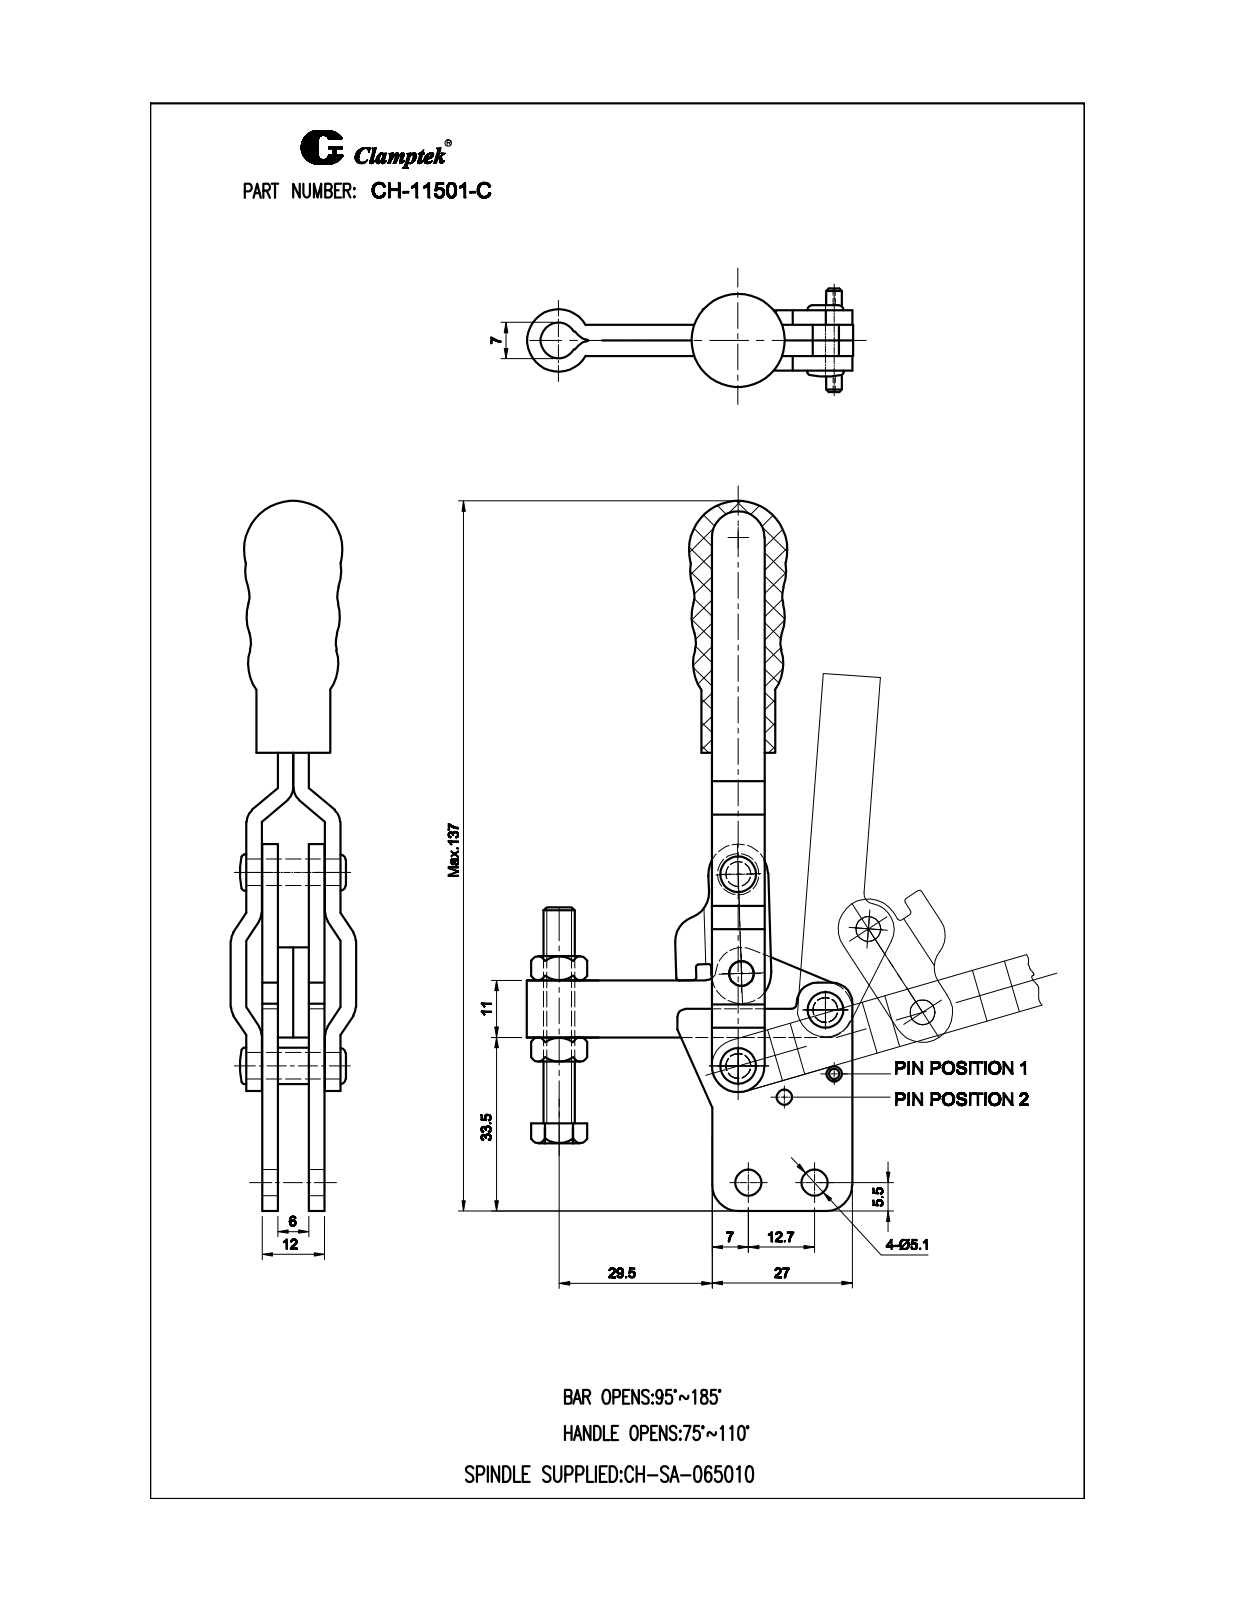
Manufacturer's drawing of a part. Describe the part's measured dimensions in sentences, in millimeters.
The part is named "CH-11501-B-01 STRAIGHT BASE; CH-11501-C-02 BAR; CH-11502-B-07; CH-11502-B-08 (+8 more)". Its 3-D file was written by "SolidWorks 2010 (CONFIG_CONTROL_DESIGN)". It is 18 solids with 514 faces: 189 planar, 156 cylindrical and 169 other. Overall it measures 140 by 63.17 by 24.98 millimeters. Its volume is 32 849 cubic millimeters and its surface area 27 603 square millimeters. Round holes: 16 of diameter 4.8, 4 of diameter 5.1, 3 of diameter 3, 2 of diameter 3.3, 1 of diameter 2, 1 of diameter 5, 1 of diameter 6.5. Round bosses or shafts: 1 of diameter 18.76, 1 of diameter 8, 1 of diameter 6, 1 of diameter 4.8, 1 of diameter 3. Partial cylindrical surfaces (rounded edges, fillets, slot ends): 16 of radius 3, 6 of radius 5, 5 of radius 5.1, 4 of radius 4, 4 of radius 5.8, 2 of radius 1, 2 of radius 1.5, 2 of radius 2. The main face-to-face distances are 3, 6, 9, 3.01, 6.1, 2.99, 3.1, 6.01, 5.9, 2.9. The hole center spacings are 31.22, 37, 17.7, 19.2, 26.35, 37.01, 42.78, 17.69.
